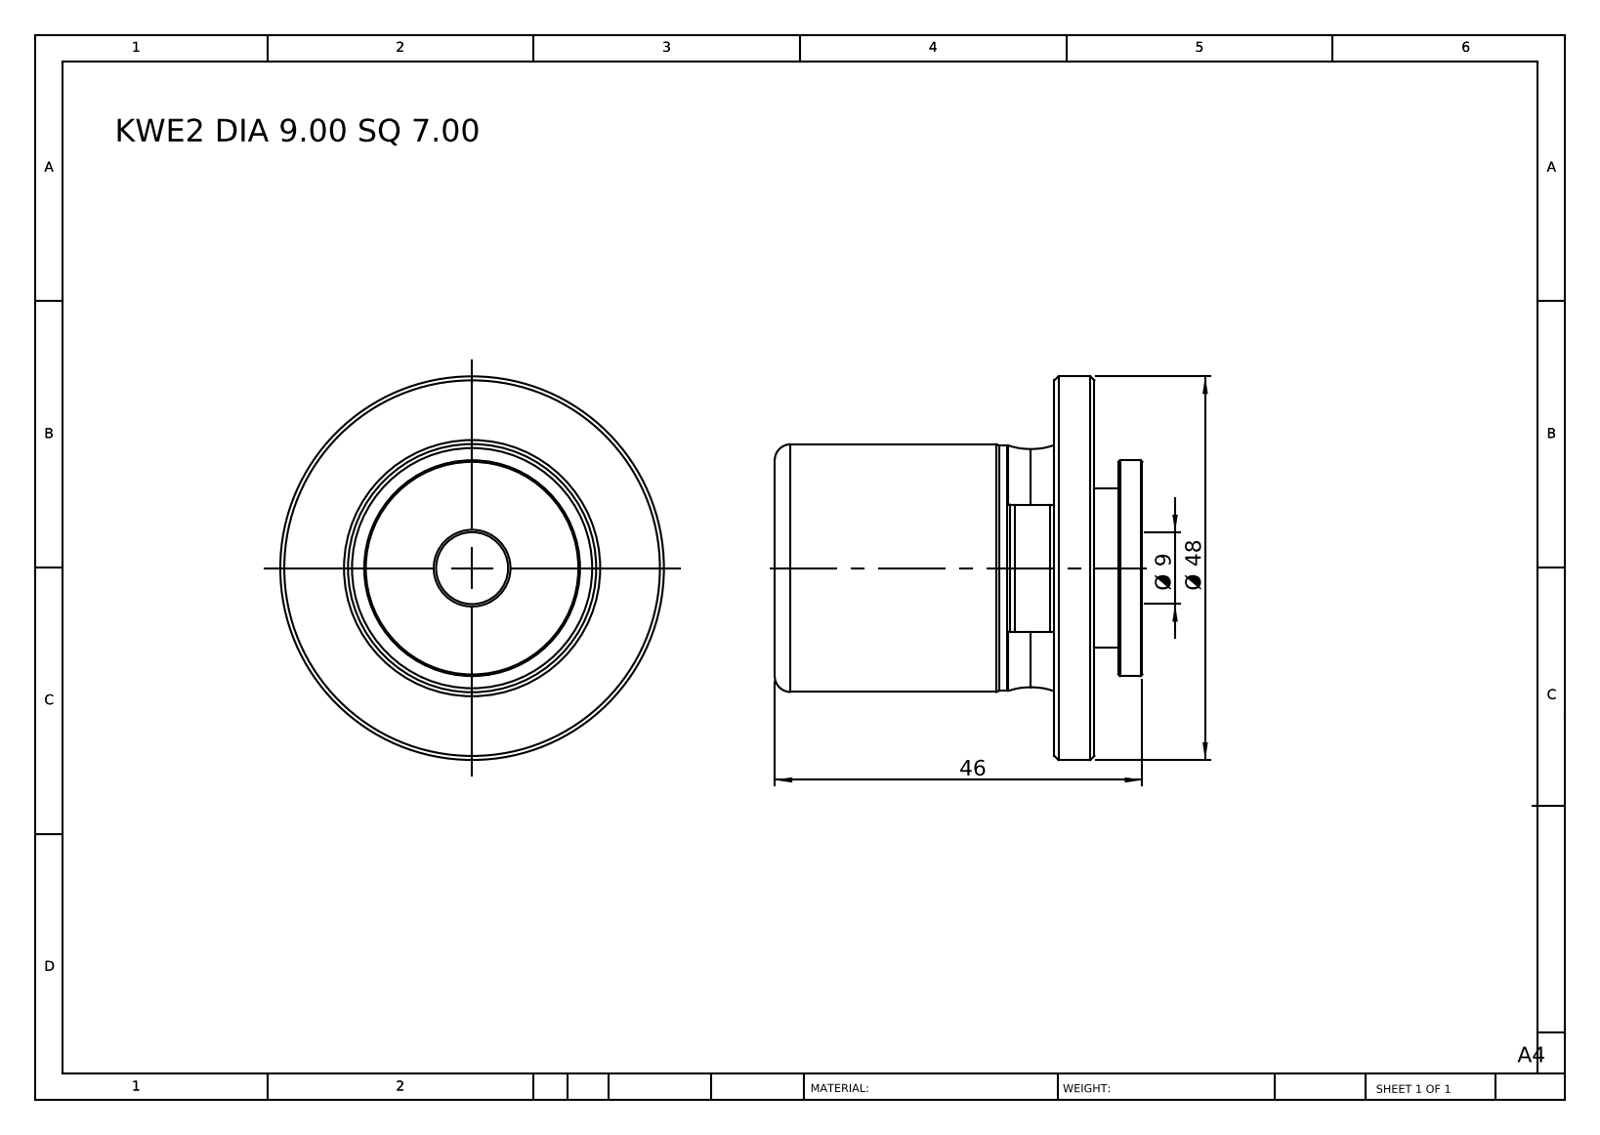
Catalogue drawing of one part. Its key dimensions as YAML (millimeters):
part_name: "KWE2 DIA 9.00 SQ 7.00"
step_written_by: "SolidWorks 2014 (CONFIG_CONTROL_DESIGN)"
units: millimeters
bodies: {solids: 1, faces: 61, planar: 13, cylindrical: 18, other: 30}
overall_size: [48, 48, 46]
volume: 36806
surface_area: 9538
round_holes:
  - {diameter: 9, count: 1}
round_bosses_or_shafts:
  - {diameter: 48, count: 1}
  - {diameter: 31, count: 1}
  - {diameter: 30.7, count: 1}
  - {diameter: 27, count: 1}
  - {diameter: 20, count: 1}
partial_cylinders:
  - {radius: 15.53, count: 1}
  - {radius: 19.9, count: 1}
face_to_face_distances: [5, 35, 40, 46, 11, 6, 3, 43, 8, 29.5]
